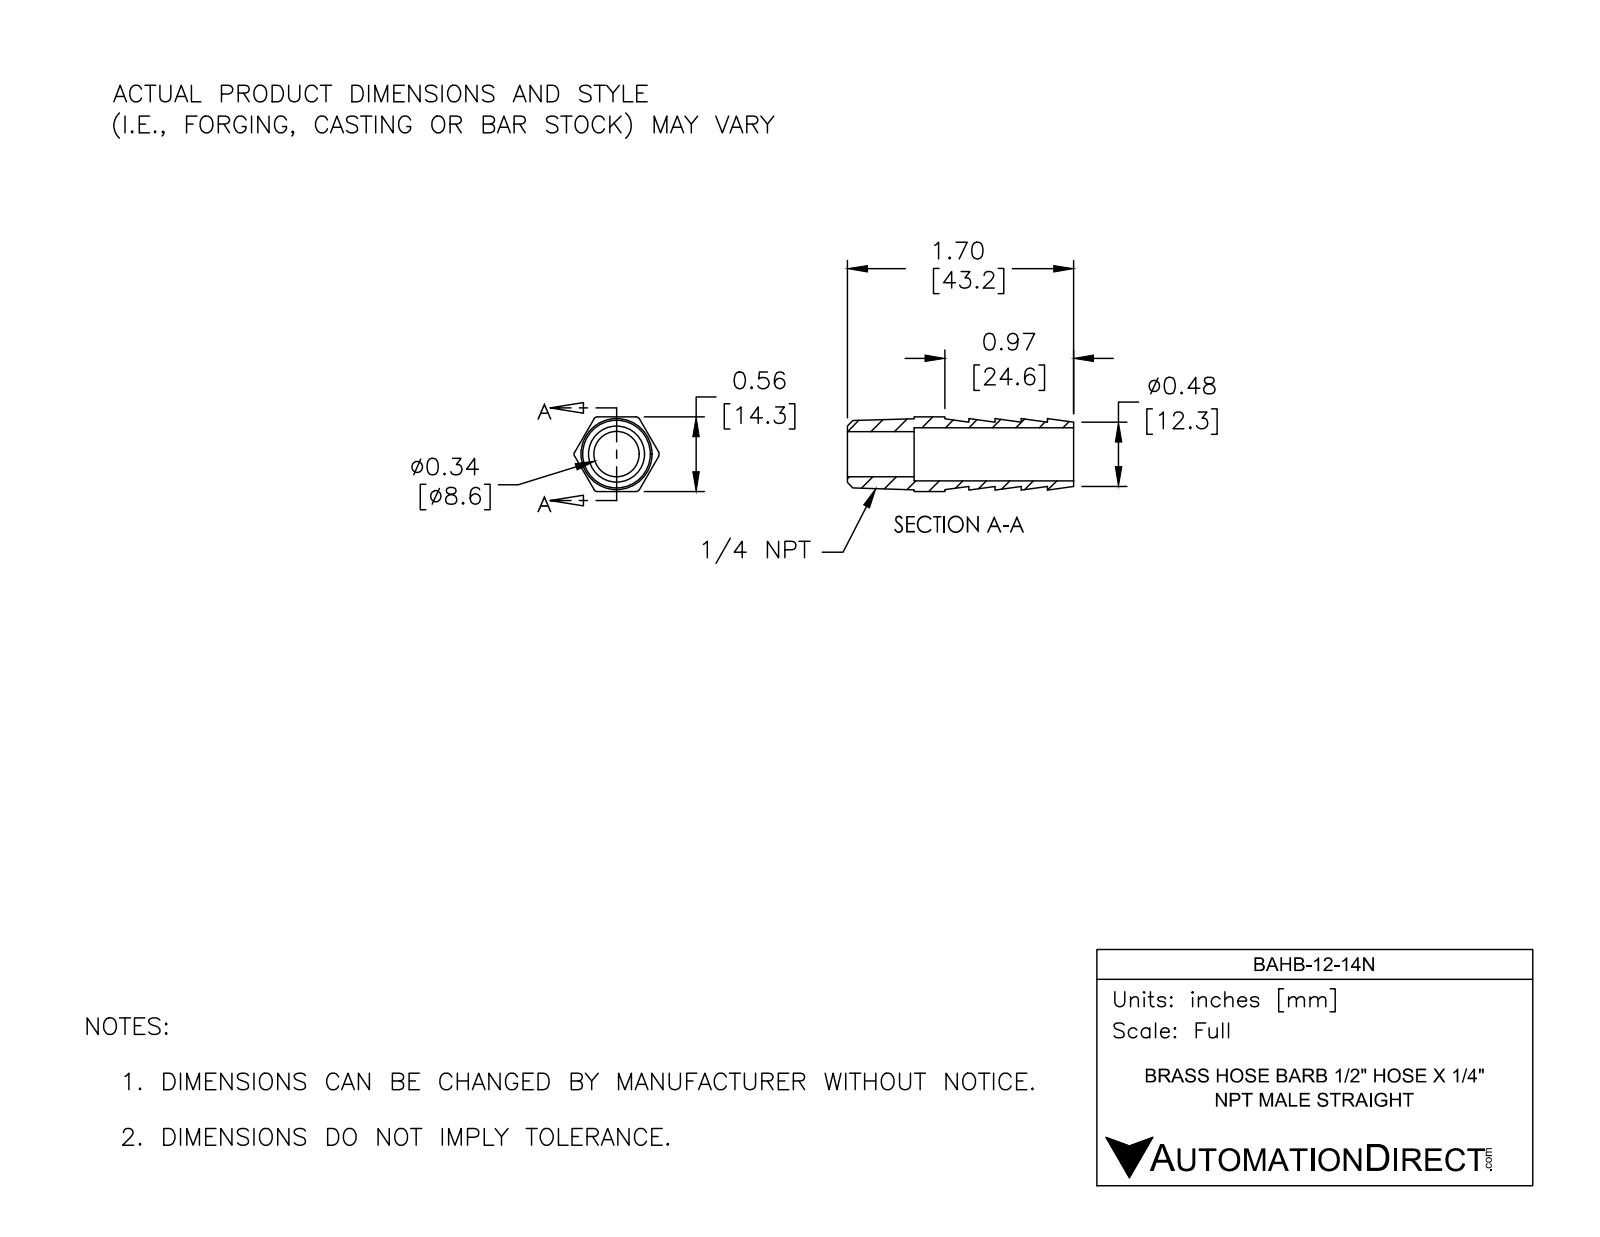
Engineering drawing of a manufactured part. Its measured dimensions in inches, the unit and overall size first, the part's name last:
Units: inches
Overall size (bounding box): 1.701 × 0.64 × 0.562
Round holes (diameter × count): ⌀0.34 ×1, ⌀0.4 ×1
Partial cylindrical surfaces — rounded edges, fillets, slot ends (radius × count): R0.03 ×6
Main face-to-face distances: 0.562, 0.197, 0.591, 0.394, 1.2, 0.968, 0.232, 1.701, 0.733, 0.501
Volume: 0.171 in³ · Surface area: 5.314 in²
Bodies: 1 solid, 39 faces (15 planar, 10 cylindrical, 14 other)
Part name (STEP PRODUCT): BAHB-12-14N
STEP written by: SolidWorks 2017 (AUTOMOTIVE_DESIGN)
